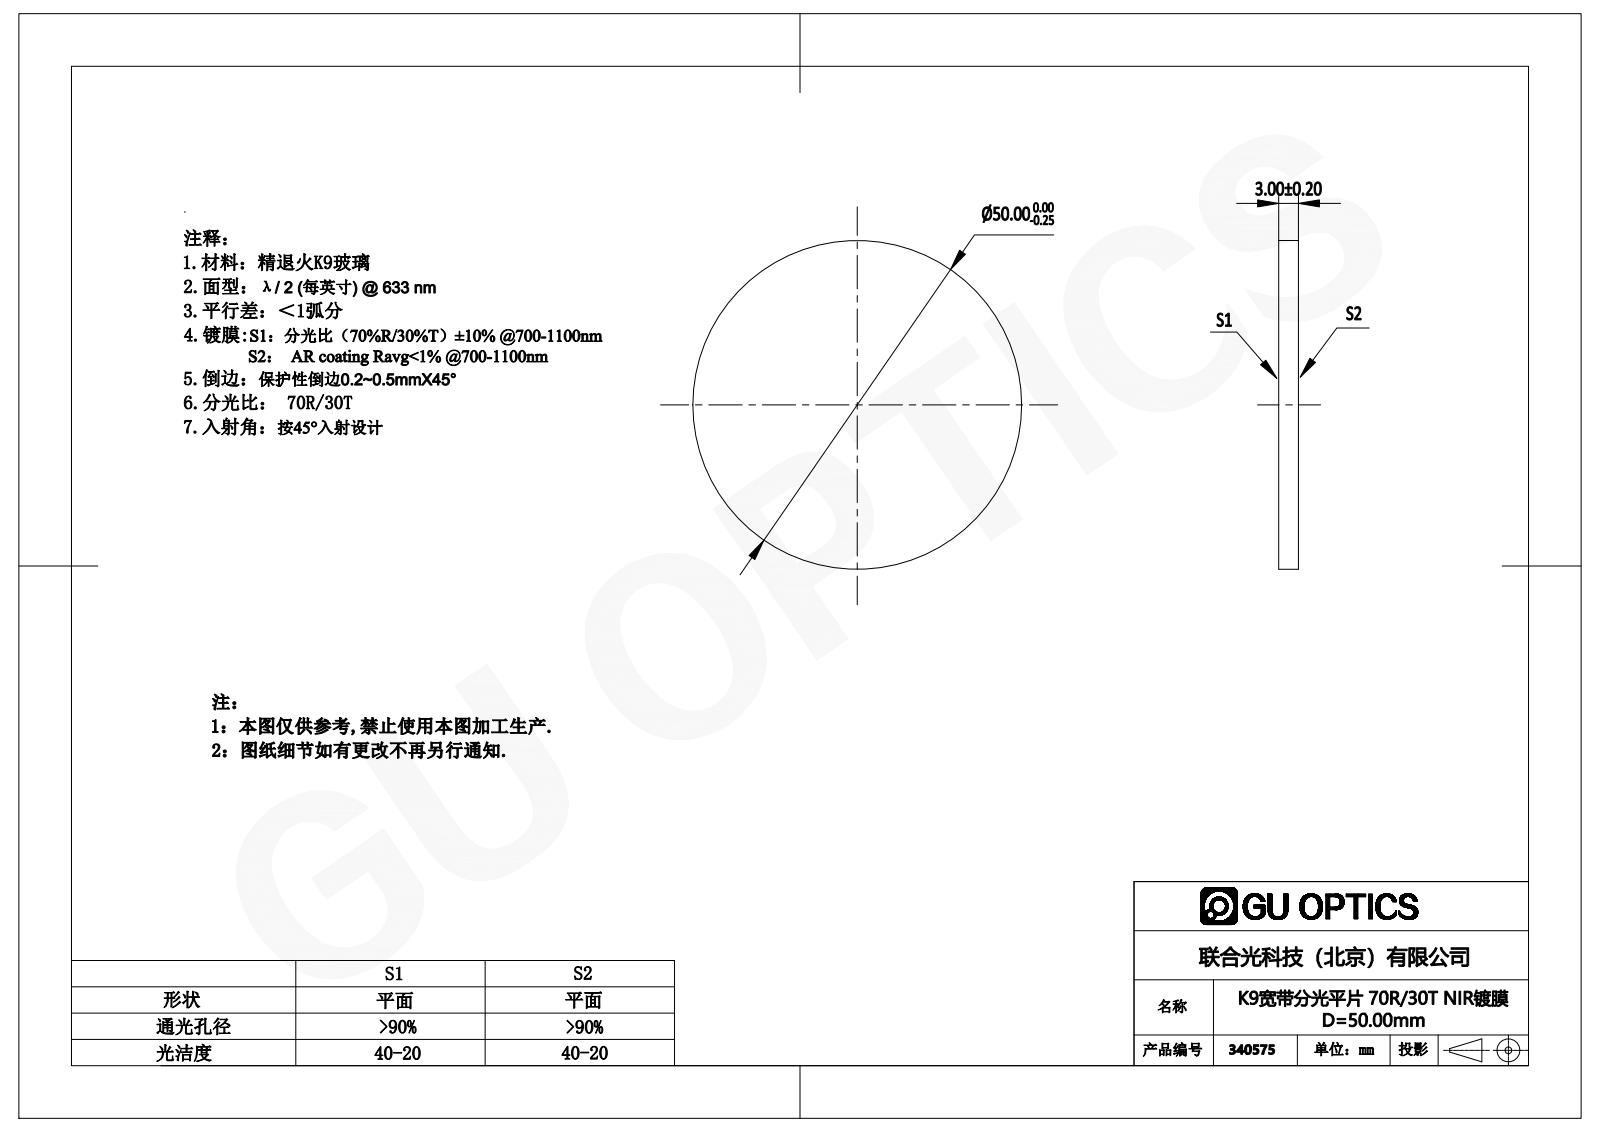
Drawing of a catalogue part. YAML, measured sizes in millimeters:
part_name: "340528"
step_written_by: "SolidWorks 2016 (CONFIG_CONTROL_DESIGN)"
units: millimeters
bodies: {solids: 1, faces: 4, planar: 2, cylindrical: 2, other: 0}
overall_size: [50, 50, 3]
volume: 5890
surface_area: 4398
round_bosses_or_shafts:
  - {diameter: 50, count: 1}
face_to_face_distances: [3]
